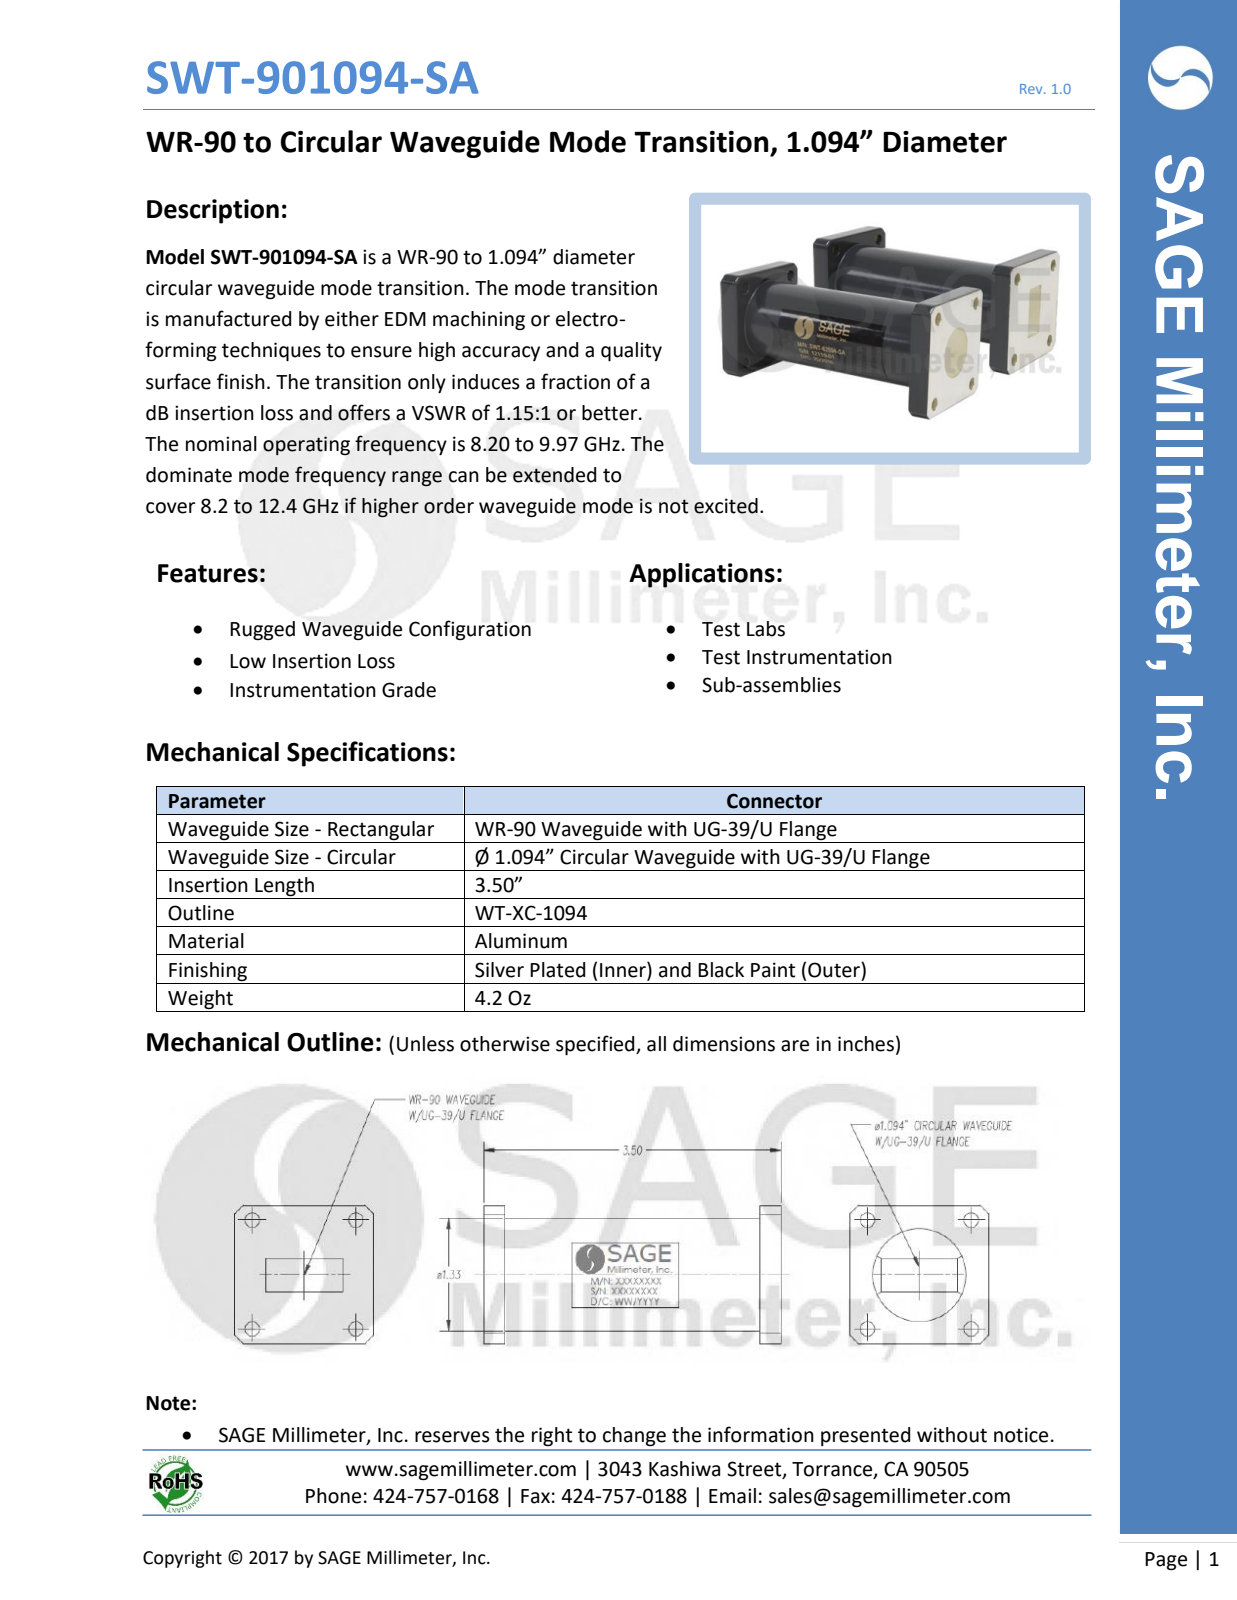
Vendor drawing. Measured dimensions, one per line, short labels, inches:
name: SWT-901094-SA
written by: SolidWorks 2021 (CONFIG_CONTROL_DESIGN)
unit: in
bodies: 1 solid, 79 faces (53 planar, 18 cylindrical, 8 other)
size: 3.5 × 1.63 × 1.63
volume: 5.422 in³; area: 24.01 in²
holes: 4× ⌀0.17
bosses: 1× ⌀1.33
face distances: 0.25, 3.25, 3.5, 3.49, 0.24, 3.24, 1.63, 3, 3.48, 2.298
hole spacings: 1.22, 1.28, 1.768
